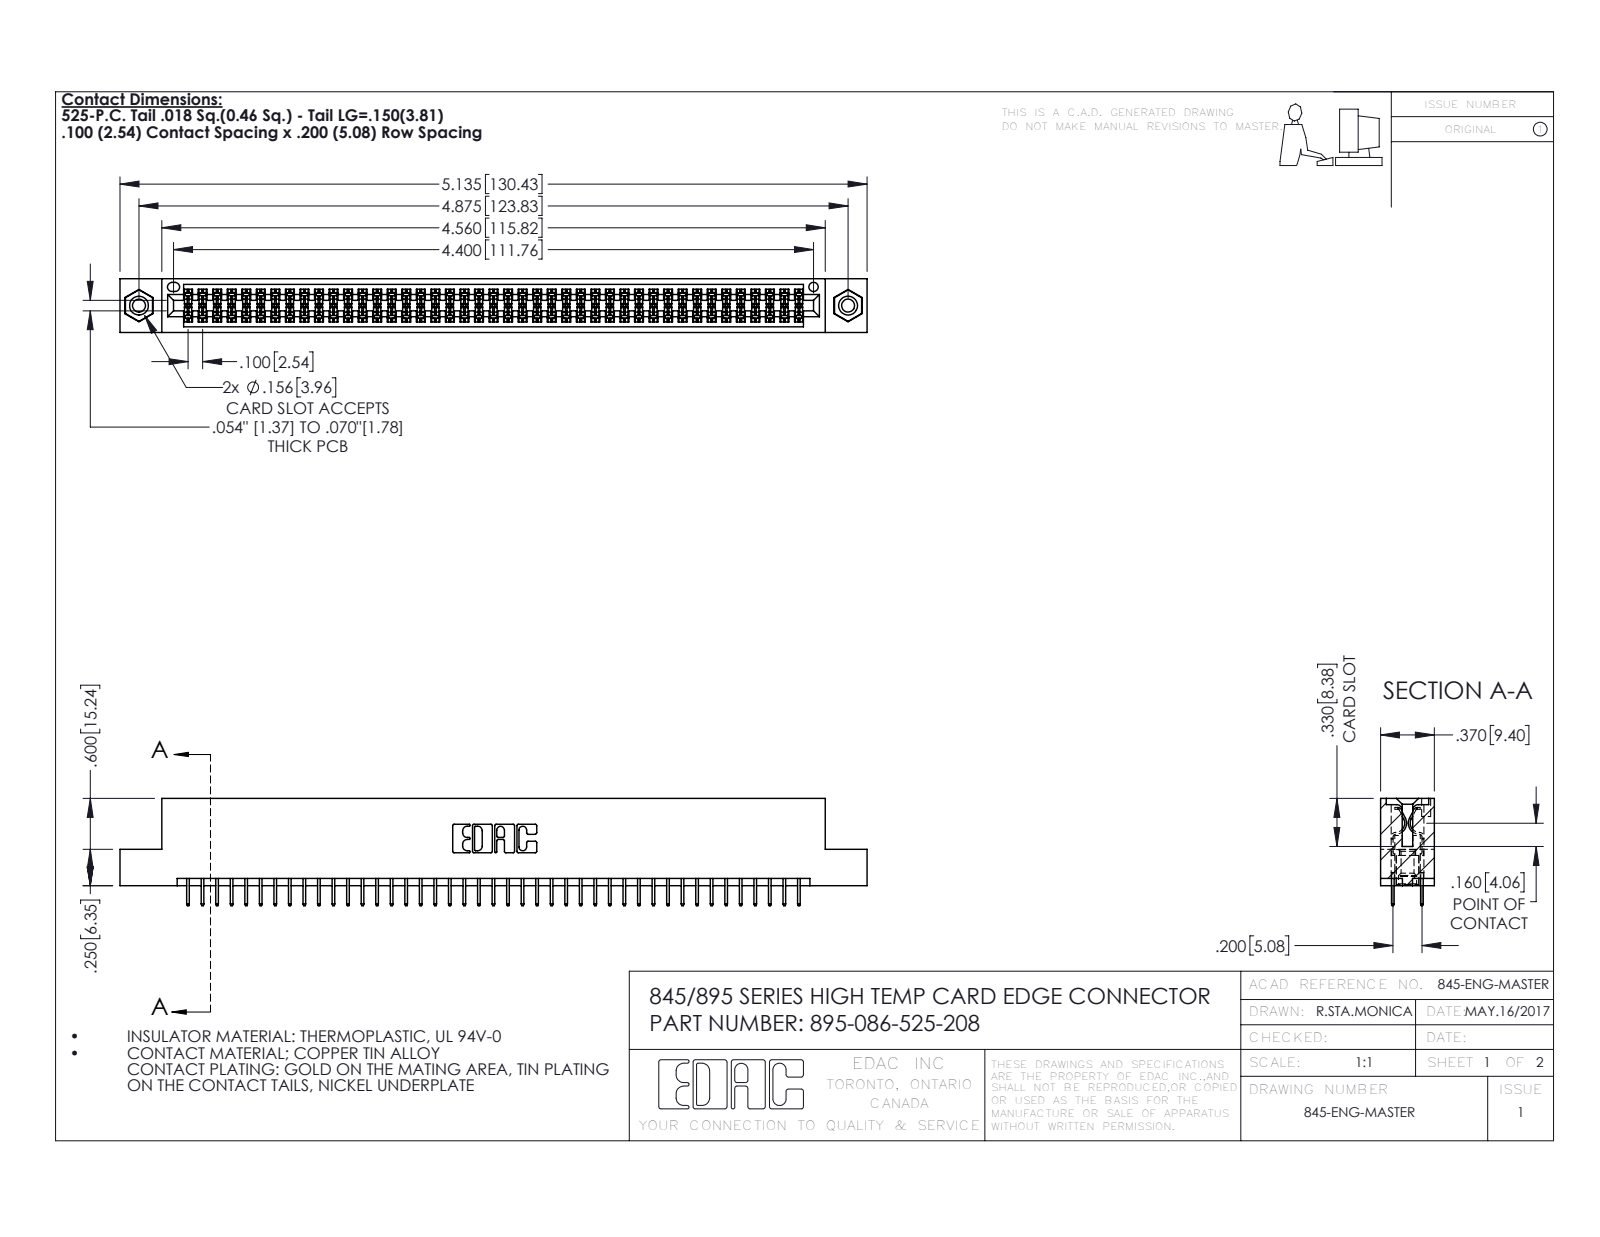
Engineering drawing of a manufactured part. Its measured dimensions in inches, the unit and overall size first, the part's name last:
Units: inches
Overall size (bounding box): 5.135 × 0.737 × 0.37
Round holes (diameter × count): ⌀0.089 ×2, ⌀0.125 ×2, ⌀0.156 ×2, ⌀0.064 ×1
Round bosses / shafts (diameter × count): ⌀0.155 ×2
Partial cylindrical surfaces — rounded edges, fillets, slot ends (radius × count): R0.006 ×172, R0.01 ×22, R0.007 ×6, R0.031 ×6, R0.026 ×3, R0.014 ×2, R0.019 ×2, R0.022 ×2
Main face-to-face distances: 0.072, 0.298, 0.2, 0.37, 0.098, 0.272, 0.025, 0.225, 0.072, 0.175
Hole centre spacings: 0.27, 4.639, 4.875
Volume: 0.765 in³ · Surface area: 28.1 in²
Bodies: 89 solids, 4830 faces (3466 planar, 1348 cylindrical, 16 other)
Part name (STEP PRODUCT): 345 Part_Flush Mounting Lugs - 0.156 Dia-TI; 395-086-525-208; 345-250-001_345-250-003-102; 345-292-001_345-293-125
STEP written by: SolidWorks 2020 (CONFIG_CONTROL_DESIGN)
